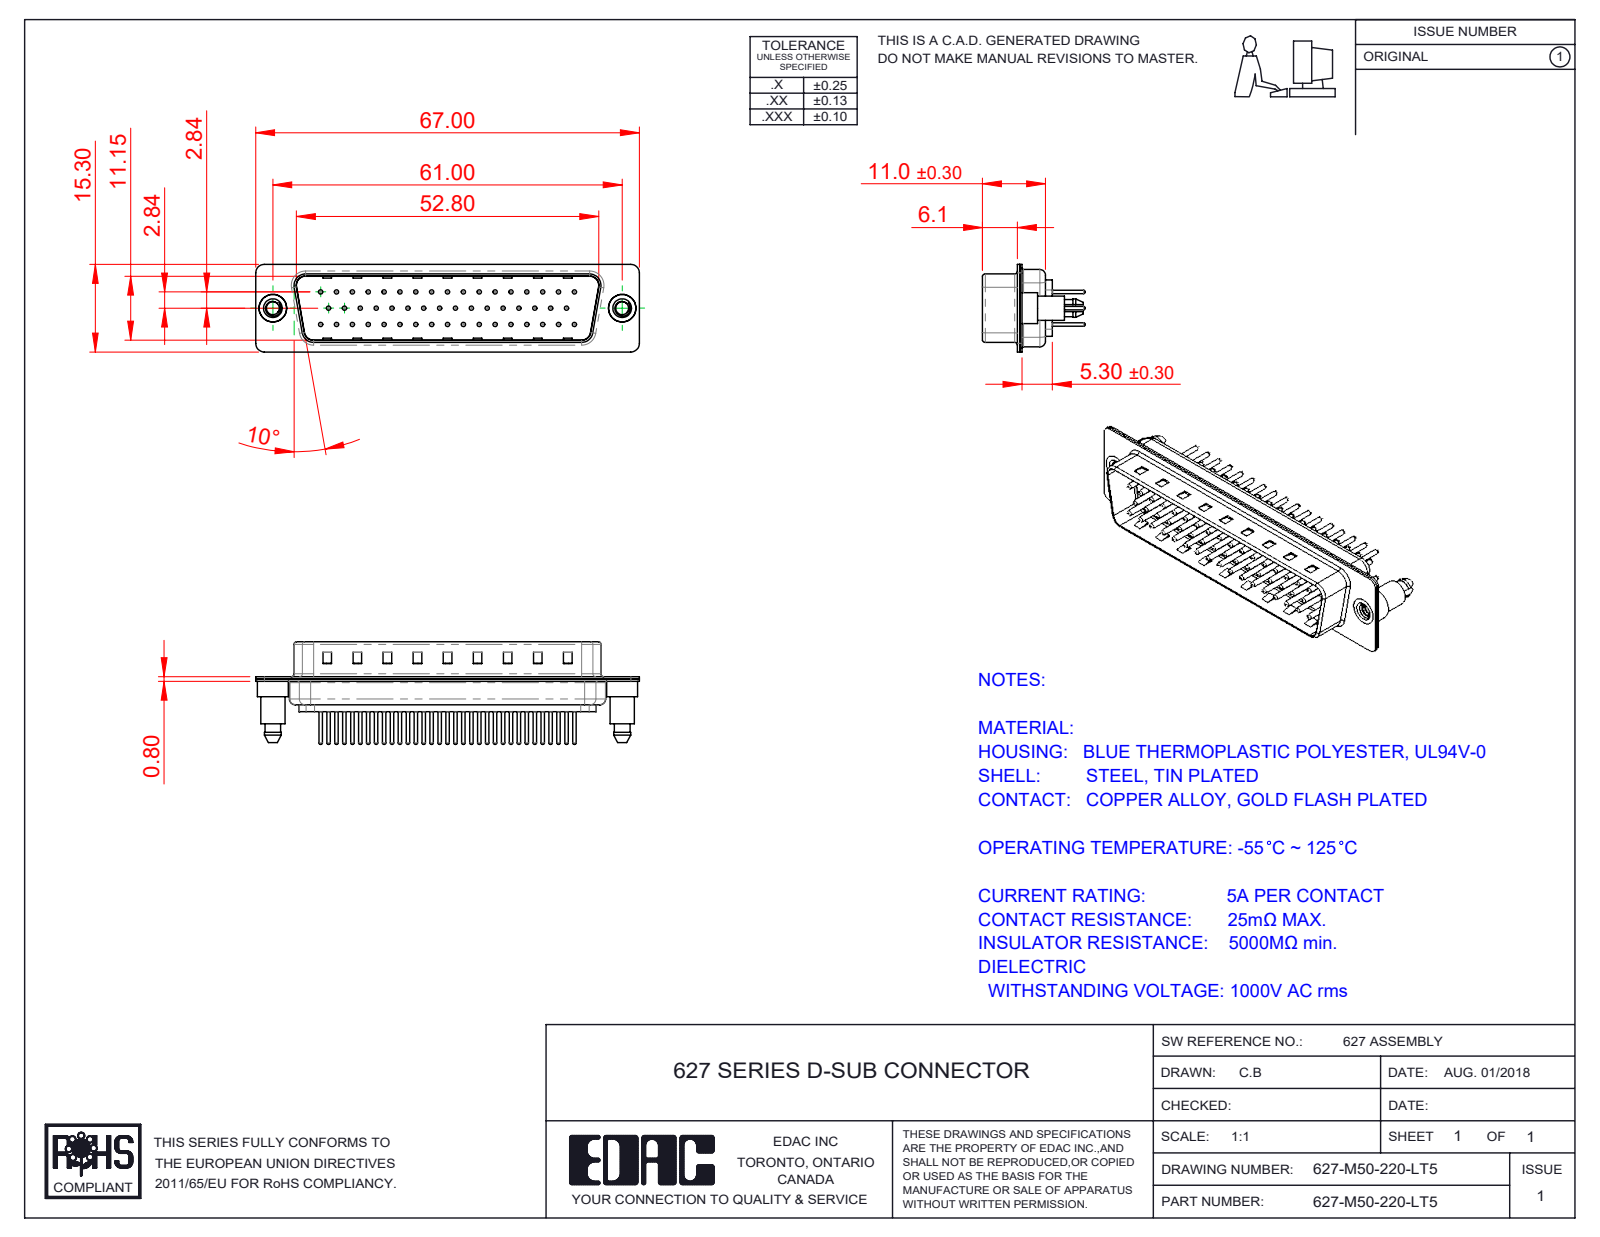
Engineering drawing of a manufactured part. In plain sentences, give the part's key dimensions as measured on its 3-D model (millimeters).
The part is named "627M Contact Row 2_20; 627-M50-220-LT5; 627M Housing_50 Contacts; 627M Shell Front_50 Contacts (+4 more)". Its 3-D file was written by "SolidWorks 2020 (CONFIG_CONTROL_DESIGN)". It is 55 solids with 2312 faces: 569 planar, 873 cylindrical and 870 other. Overall it measures 67 by 17.9 by 15.3 millimeters. Its volume is 4 659 cubic millimeters and its surface area 11 032 square millimeters. Round holes: 50 of diameter 0.75, 50 of diameter 1.6, 50 of diameter 2, 2 of diameter 2.26, 2 of diameter 4, 2 of diameter 4.8. Round bosses or shafts: 50 of diameter 1.5, 50 of diameter 0.6, 2 of diameter 5.4, 2 of diameter 4.9, 2 of diameter 4.25. Partial cylindrical surfaces (rounded edges, fillets, slot ends): 18 of radius 1.5, 12 of radius 2, 10 of radius 1.6, 8 of radius 0.5, 4 of radius 0.25, 4 of radius 0.6, 4 of radius 0.65, 4 of radius 0.9. The main face-to-face distances are 0.4, 11.55, 5.7, 6.1, 0.78, 0.77, 12.33, 5.3, 12.32, 13.1. The hole center spacings are 3.16, 2.77, 5.54, 8.31, 11.08, 13.85, 16.62, 5.03.
